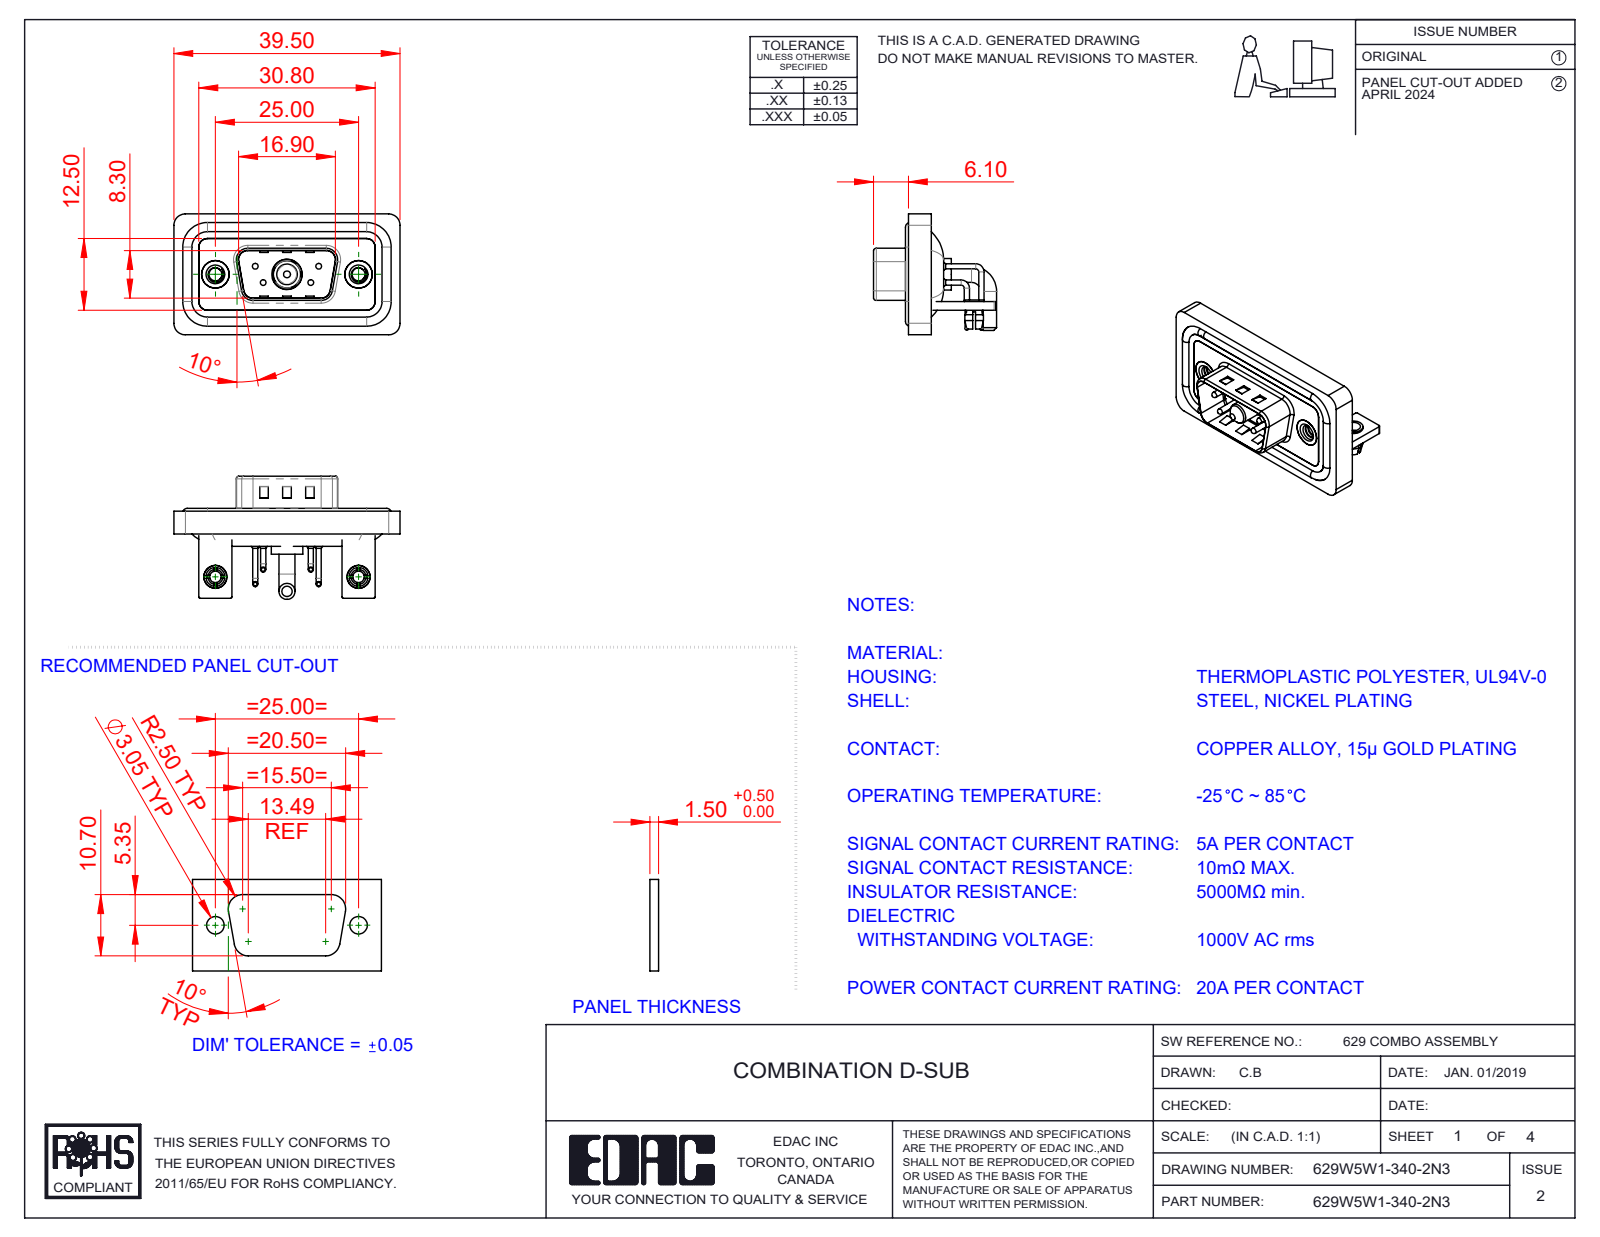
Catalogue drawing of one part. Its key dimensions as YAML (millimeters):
part_name: "629Combo Shell Front_09 Contacts; 629Combo Threaded Rivet_3; 629Combo Shell Rear_09 Contacts; 629Combo Stabilizer Bracket (+7 more)"
step_written_by: "SolidWorks 2023 (CONFIG_CONTROL_DESIGN)"
units: millimeters
bodies: {solids: 17, faces: 1026, planar: 479, cylindrical: 395, other: 152}
overall_size: [39.5, 21.5, 21.1]
volume: 4790
surface_area: 7961
round_holes:
  - {diameter: 2, count: 6}
  - {diameter: 0.75, count: 4}
  - {diameter: 1.6, count: 4}
  - {diameter: 2.26, count: 2}
  - {diameter: 2.5, count: 2}
  - {diameter: 3.2, count: 2}
  - {diameter: 4, count: 2}
  - {diameter: 4.8, count: 2}
  - {diameter: 5, count: 2}
  - {diameter: 4.85, count: 1}
  - {diameter: 5.3, count: 1}
round_bosses_or_shafts:
  - {diameter: 0.9, count: 8}
  - {diameter: 1.6, count: 4}
  - {diameter: 1.5, count: 4}
  - {diameter: 1, count: 4}
  - {diameter: 0.65, count: 4}
  - {diameter: 4.9, count: 2}
  - {diameter: 4, count: 2}
  - {diameter: 3.4, count: 2}
partial_cylinders:
  - {radius: 2, count: 19}
  - {radius: 1.5, count: 18}
  - {radius: 0.25, count: 16}
  - {radius: 0.5, count: 9}
  - {radius: 1.6, count: 8}
  - {radius: 0.6, count: 4}
  - {radius: 0.65, count: 4}
  - {radius: 0.9, count: 4}
face_to_face_distances: [0.4, 1.5, 0.8, 2.9, 1.1, 2.1, 1.2, 1.6, 2.5, 3.7]
hole_center_spacings: [3.16, 5.72, 7.1, 12.5, 18.1, 25, 4.39, 4.4]
